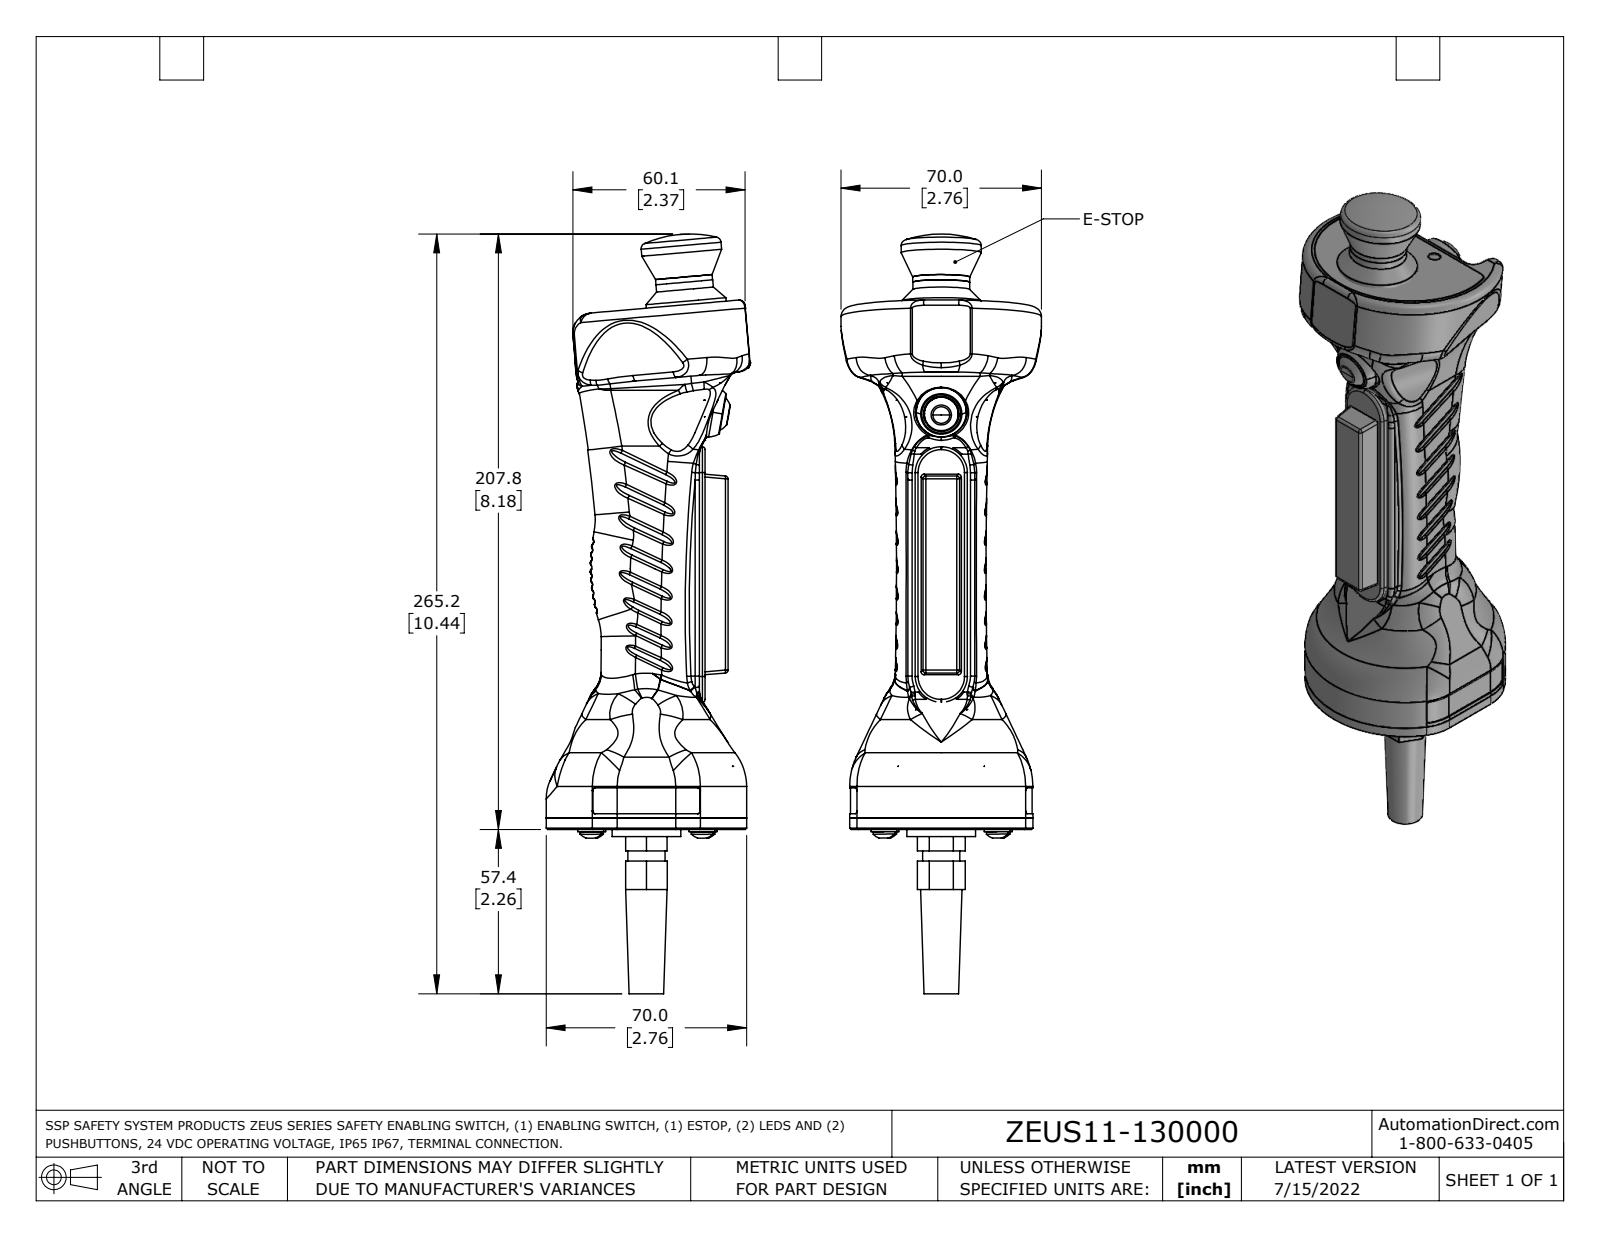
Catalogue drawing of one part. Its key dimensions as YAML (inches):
part_name: "ZEUS11-130000"
step_written_by: "SolidWorks 2021 (AUTOMOTIVE_DESIGN)"
units: inches
bodies: {solids: 22, faces: 1616, planar: 625, cylindrical: 515, other: 476}
overall_size: [10.442, 2.803, 2.756]
volume: 24.33
surface_area: 131.8
round_holes:
  - {diameter: 0.132, count: 4}
  - {diameter: 0.169, count: 4}
  - {diameter: 0.177, count: 4}
  - {diameter: 0.197, count: 4}
  - {diameter: 0.039, count: 2}
  - {diameter: 0.098, count: 2}
  - {diameter: 0.11, count: 2}
  - {diameter: 0.159, count: 2}
  - {diameter: 0.165, count: 2}
  - {diameter: 0.173, count: 2}
  - {diameter: 0.201, count: 2}
  - {diameter: 0.205, count: 2}
round_bosses_or_shafts:
  - {diameter: 0.354, count: 4}
  - {diameter: 0.295, count: 4}
  - {diameter: 0.157, count: 4}
  - {diameter: 0.039, count: 4}
  - {diameter: 0.461, count: 3}
  - {diameter: 1.102, count: 2}
  - {diameter: 0.781, count: 2}
  - {diameter: 0.689, count: 2}
partial_cylinders:
  - {radius: 0.005, count: 96}
  - {radius: 0.039, count: 51}
  - {radius: 0.028, count: 48}
  - {radius: 0.008, count: 42}
  - {radius: 0.079, count: 21}
  - {radius: 0.006, count: 16}
  - {radius: 0.118, count: 10}
  - {radius: 0.031, count: 7}
face_to_face_distances: [0.157, 0.079, 0.02, 0.014, 0.065, 0.059, 0.098, 0.039, 0.177, 0.571]
hole_center_spacings: [0.404, 0.63, 0.867, 1.08, 1.181, 1.531, 1.558, 0.513]
